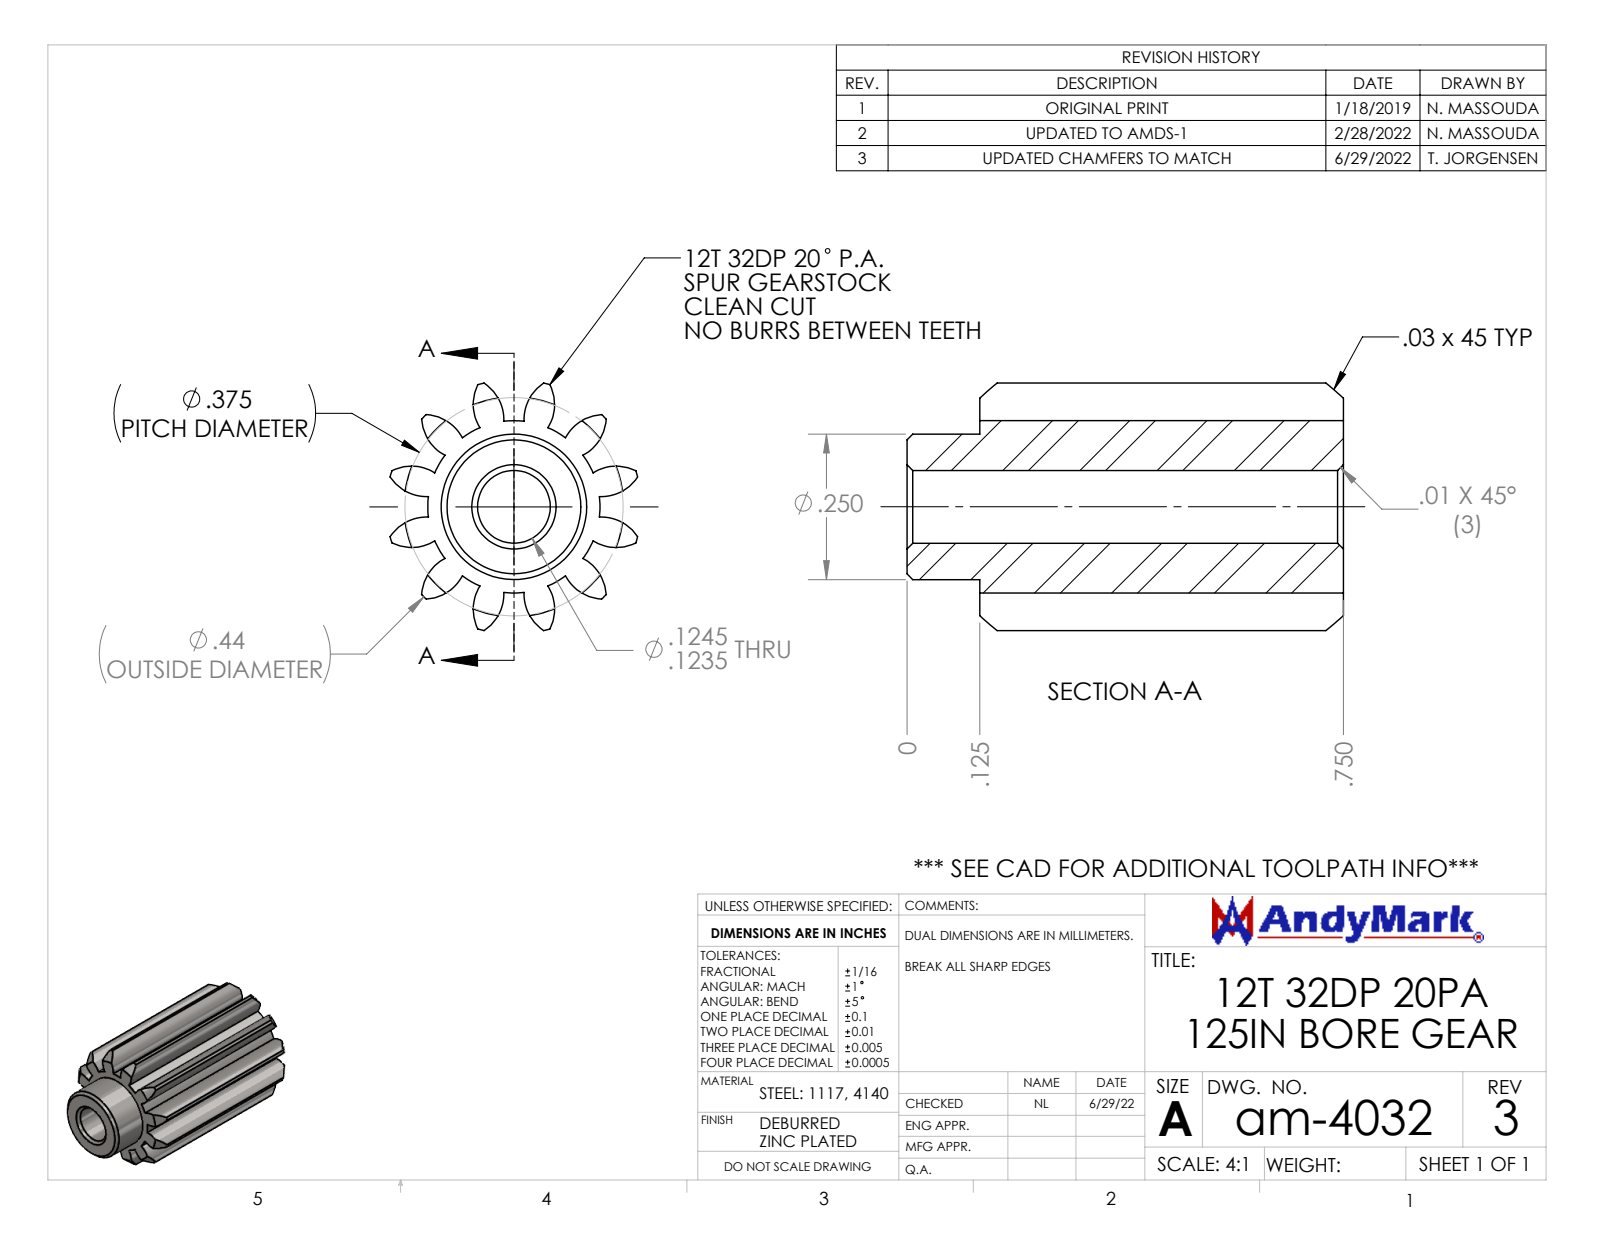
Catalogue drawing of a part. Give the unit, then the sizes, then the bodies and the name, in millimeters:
Units: millimetres
Overall size (bounding box): 19.1 × 10.8 × 10.8
Round holes (diameter × count): ⌀3.2 ×1
Round bosses / shafts (diameter × count): ⌀6.4 ×1
Partial cylindrical surfaces — rounded edges, fillets, slot ends (radius × count): R1.9 ×24, R3.8 ×1, R5.6 ×1
Main face-to-face distances: 15.9, 19.1, 3.2
Volume: 1 000 mm³ · Surface area: 1 319 mm²
Bodies: 1 solid, 90 faces (3 planar, 57 cylindrical, 30 other)
Part name (STEP PRODUCT): am-4032 12T 32DP 125 Bore Gear
STEP written by: SolidWorks 2022 (CONFIG_CONTROL_DESIGN)
